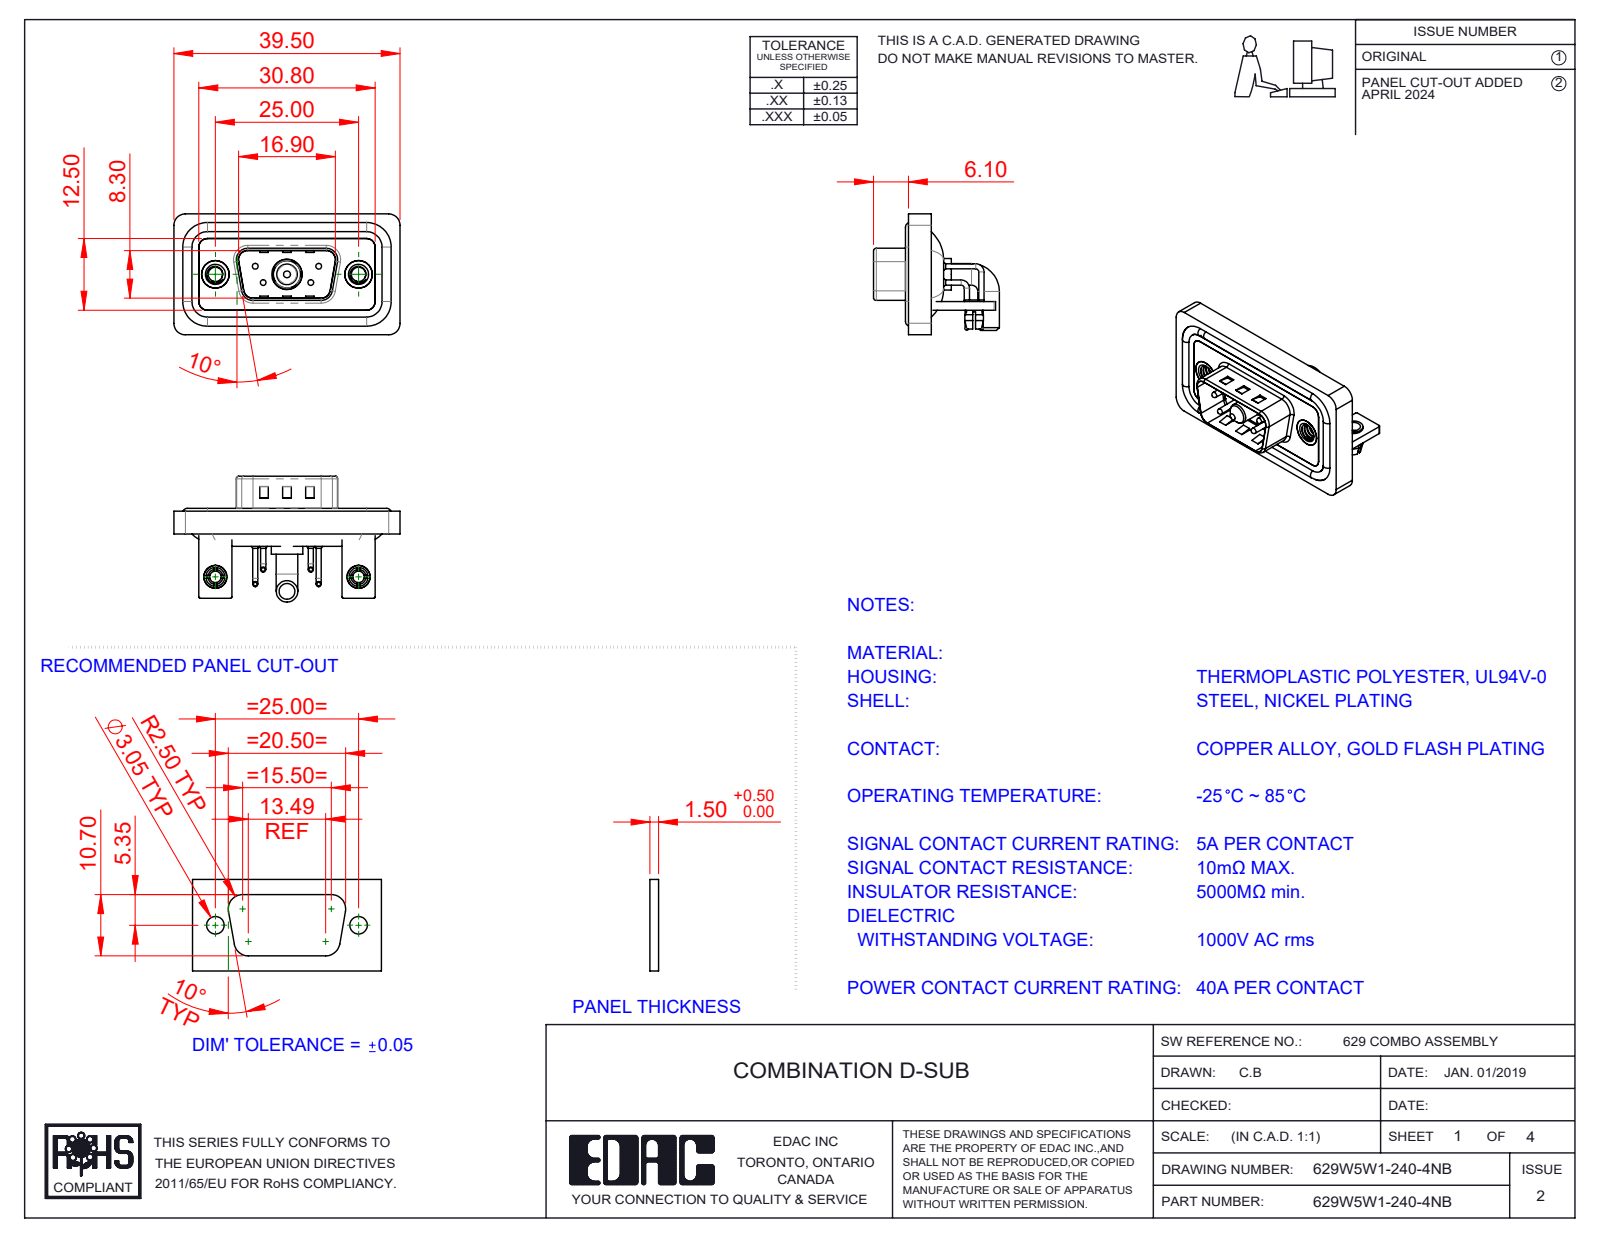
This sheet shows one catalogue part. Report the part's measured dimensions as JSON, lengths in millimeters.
{"part_name": "629Combo Stabilizer Bracket; 629Combo Shell Rear_09 Contacts; 629Combo Board Lock; 629Combo Threaded Rivet_B (+7 more)", "step_written_by": "SolidWorks 2023 (CONFIG_CONTROL_DESIGN)", "units": "millimeters", "bodies": {"solids": 17, "faces": 1024, "planar": 479, "cylindrical": 395, "other": 150}, "overall_size": [39.5, 21.98, 21.1], "volume_mm3": 4857, "surface_area_mm2": 8006, "round_holes": [[2, 6], [0.75, 4], [1.6, 4], [2.5, 4], [3.2, 2], [4, 2], [4.8, 2], [5, 2], [4.85, 1], [5.3, 1]], "round_bosses_or_shafts": [[0.9, 8], [1.6, 4], [1.5, 4], [1, 4], [0.65, 4], [4.9, 2], [4, 2], [3.75, 2]], "partial_cylinders_radius": [[2, 19], [1.5, 18], [0.25, 16], [0.5, 9], [1.6, 8], [0.6, 4], [0.65, 4], [0.9, 4]], "face_to_face_distances": [0.4, 1.5, 0.8, 2.9, 1.1, 2.1, 1.2, 1.6, 2.5, 3.7], "hole_center_spacings": [3.16, 5.72, 7.1, 12.5, 18.1, 25, 4.39, 4.4]}
